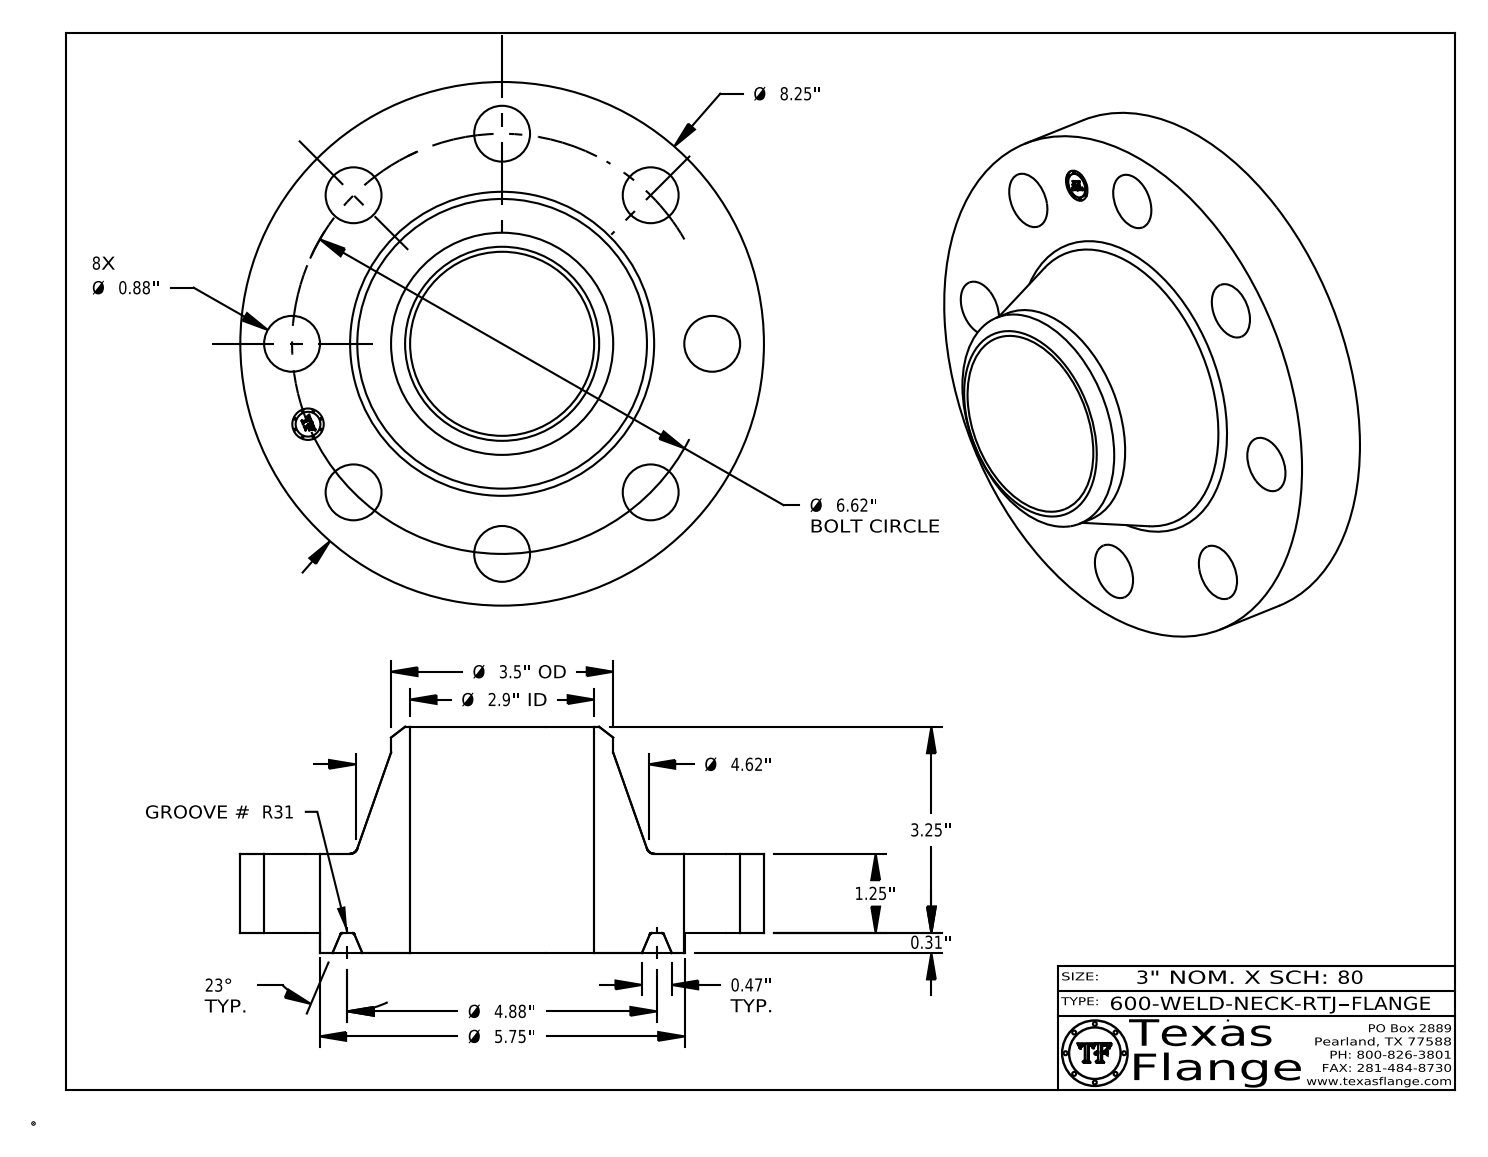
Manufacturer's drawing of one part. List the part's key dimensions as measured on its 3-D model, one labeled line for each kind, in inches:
Part name (STEP PRODUCT): 600-WELD-NECK-RTJ
STEP written by: CATIA V5 STEP AP214 (AUTOMOTIVE_DESIGN)
Units: inches
Bodies: 1 solid, 437 faces (371 planar, 52 cylindrical, 14 other)
Overall size (bounding box): 8.25 × 8.25 × 3.563
Volume: 68.22 in³ · Surface area: 205.7 in²
Round holes (diameter × count): ⌀0.88 ×8, ⌀0.495 ×1, ⌀2.9 ×1
Round bosses / shafts (diameter × count): ⌀0.03 ×8, ⌀8.25 ×1, ⌀5.75 ×1, ⌀3.5 ×1, ⌀0.39 ×1
Main face-to-face distances: 1.25, 0.313, 1.563, 3.563, 3.25, 2, 0.015, 1.548, 1.235, 2.015
Hole centre spacings: 3.31, 2.533, 6.116, 4.681, 4.681, 1.291, 3.678, 6.493
